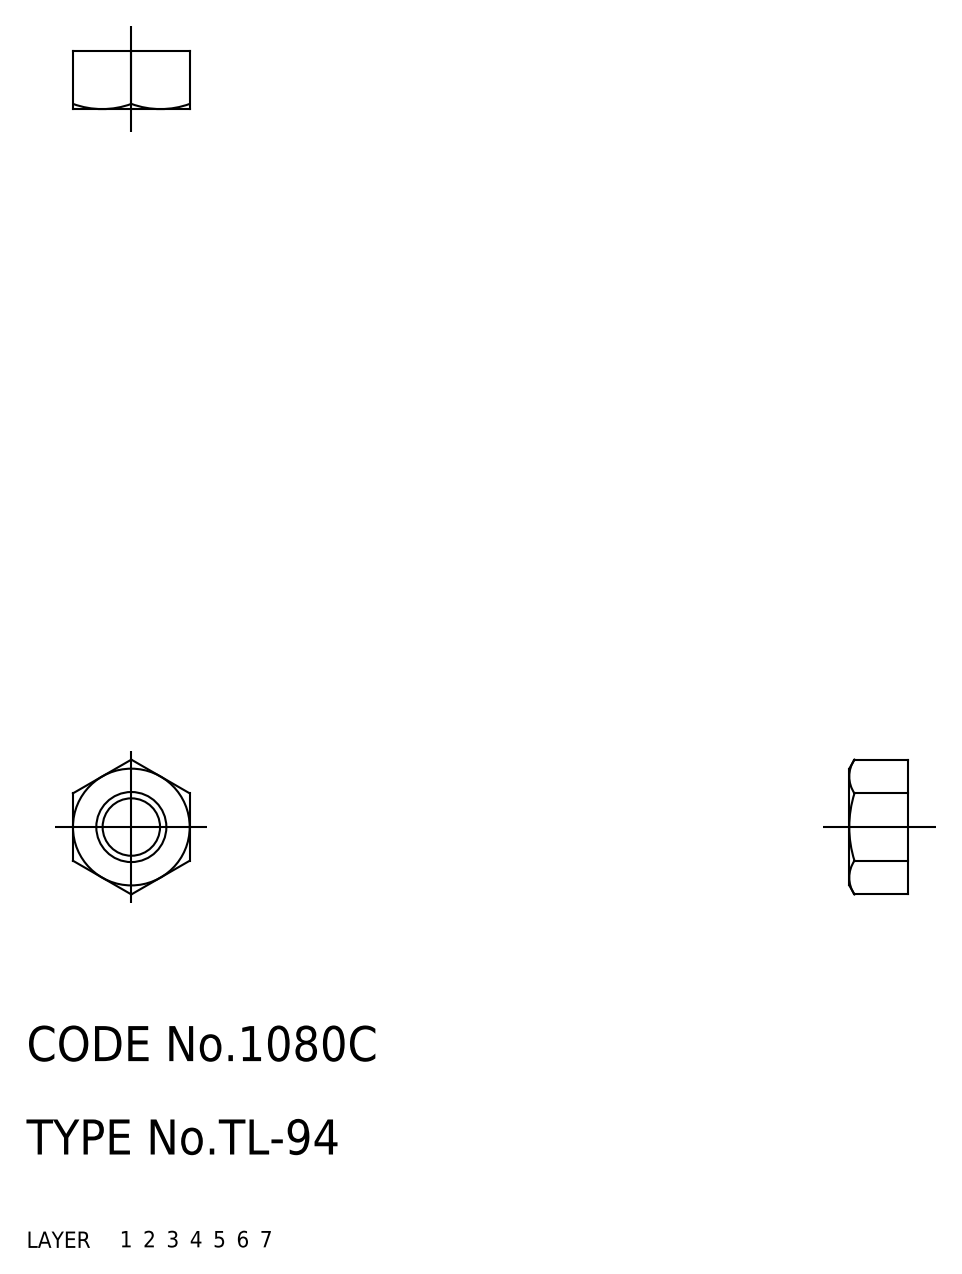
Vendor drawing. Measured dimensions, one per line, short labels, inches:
name: nut
written by: CADfix (AUTOMOTIVE_DESIGN)
unit: in
bodies: 1 solid, 16 faces (0 planar, 0 cylindrical, 16 other)
size: 0.455 × 0.394 × 0.197
volume: 0.018 in³; area: 0.589 in²
